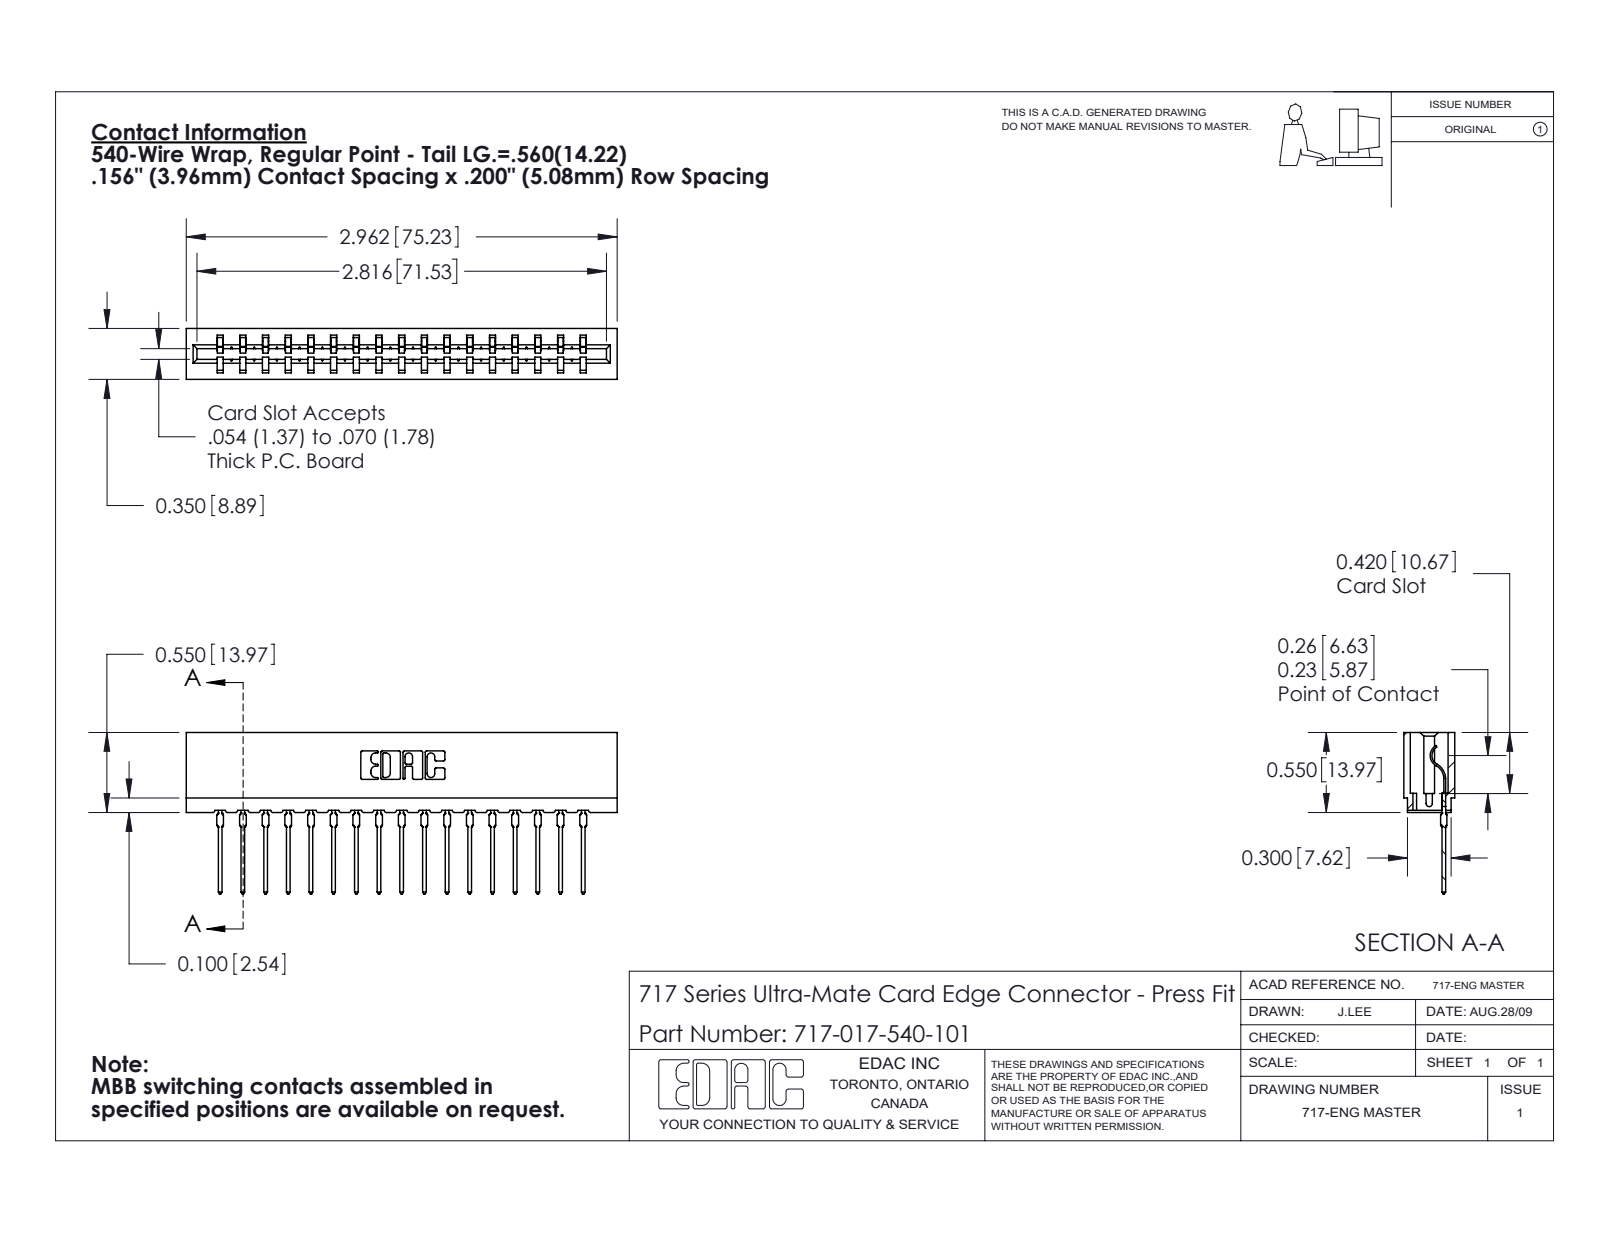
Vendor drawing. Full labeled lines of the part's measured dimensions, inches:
Part name (STEP PRODUCT): 717 Part_Insulator Option - 06; 745-292-001_540; 717-017-540-101
STEP written by: SolidWorks 2020 (CONFIG_CONTROL_DESIGN)
Units: inches
Bodies: 18 solids, 2015 faces (1210 planar, 363 cylindrical, 442 other)
Overall size (bounding box): 2.962 × 1.109 × 0.35
Volume: 0.397 in³ · Surface area: 14.05 in²
Partial cylindrical surfaces — rounded edges, fillets, slot ends (radius × count): R0.015 ×34, R0.021 ×34, R0.01 ×22, R0.007 ×6, R0.031 ×6, R0.005 ×4, R0.011 ×4, R0.026 ×3
Main face-to-face distances: 0.212, 0.138, 0.35, 0.156, 0.624, 0.468, 0.074, 0.198, 0.063, 0.287
